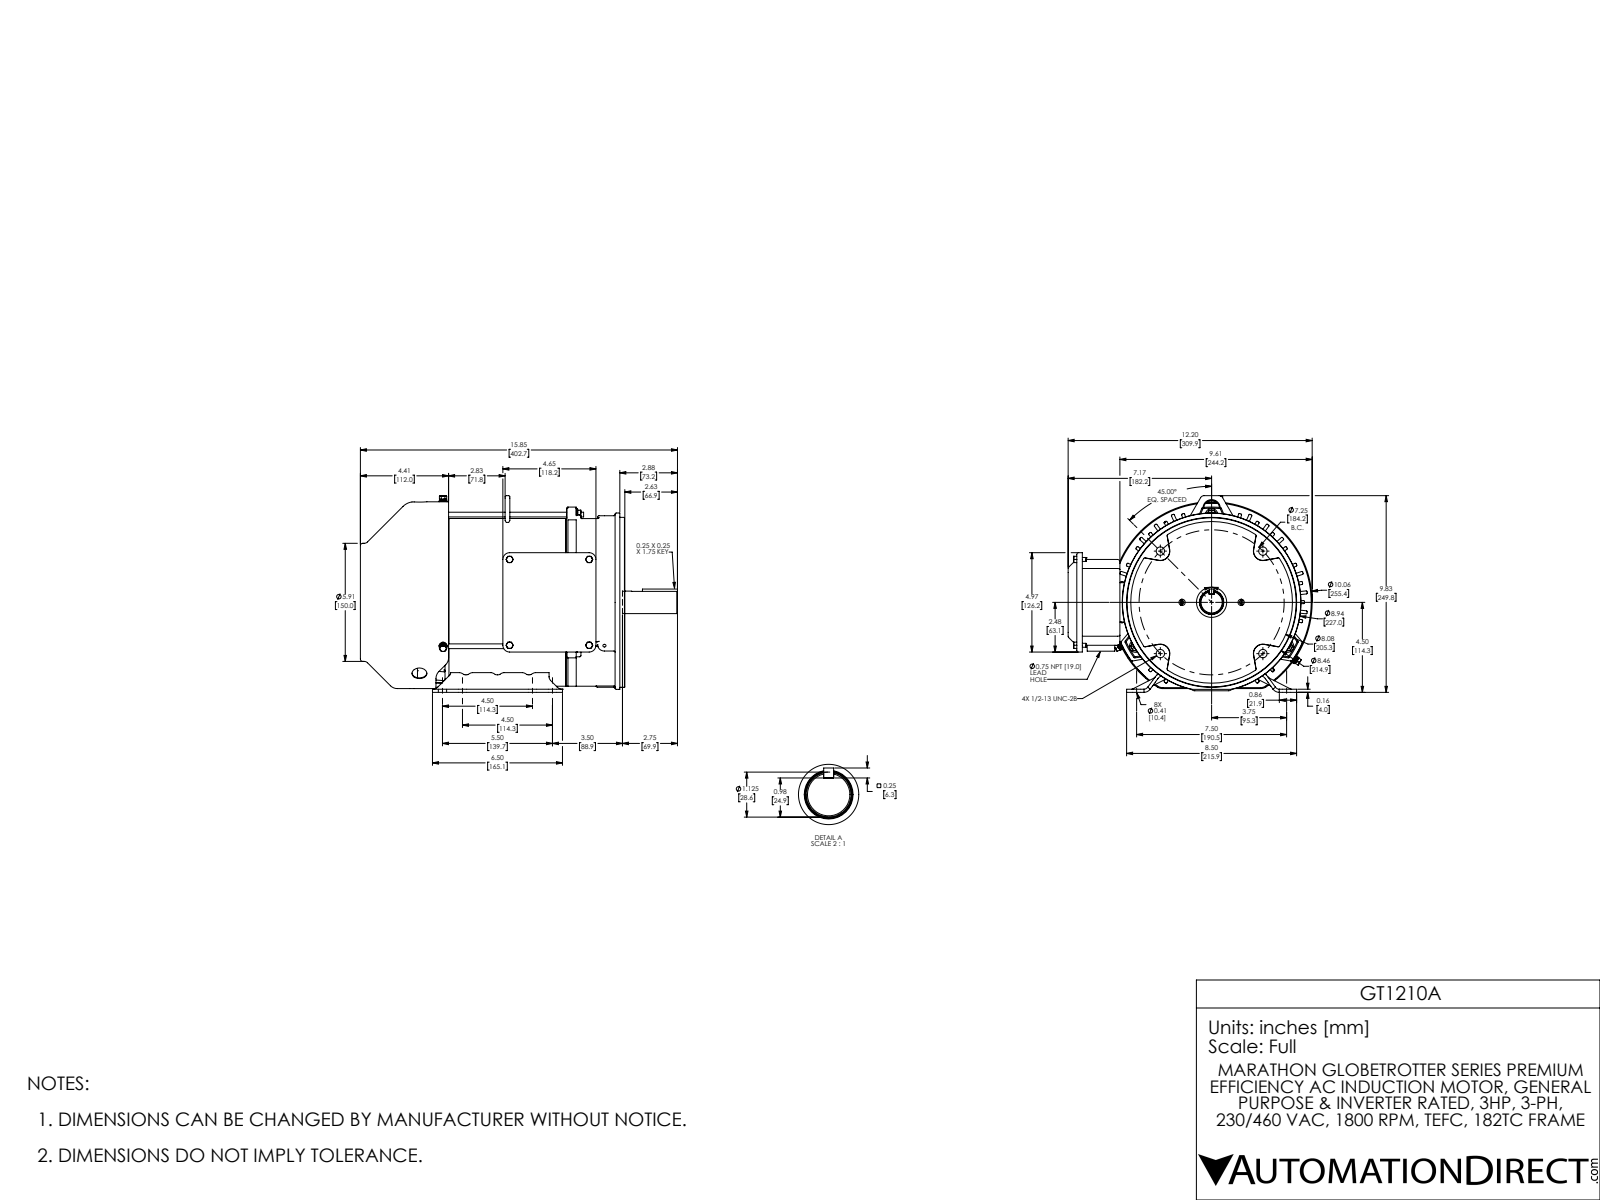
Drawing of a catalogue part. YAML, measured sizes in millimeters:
part_name: "SS600200-182TC_RevB r1 2 surfs rep Nice r3 -fan ext bell 1 R1 finext 1 -FBell b2 r1 COMB 1 COMPLETE 1 with 600198 BBELLS 1 work pre Coord RED 1"
step_written_by: "SolidWorks 2017 (AUTOMOTIVE_DESIGN)"
units: millimeters
bodies: {solids: 30, faces: 4408, planar: 645, cylindrical: 1681, other: 2082}
overall_size: [402.7, 309.9, 249.8]
volume: 4472000
surface_area: 979400
round_holes:
  - {diameter: 4.2, count: 8}
  - {diameter: 10.5, count: 8}
  - {diameter: 8, count: 6}
  - {diameter: 5, count: 4}
  - {diameter: 5.5, count: 4}
  - {diameter: 10.7, count: 4}
  - {diameter: 5.3, count: 3}
  - {diameter: 6.4, count: 3}
  - {diameter: 7, count: 3}
  - {diameter: 3.3, count: 2}
  - {diameter: 19, count: 2}
  - {diameter: 5.8, count: 1}
round_bosses_or_shafts:
  - {diameter: 5, count: 7}
  - {diameter: 15.5, count: 3}
  - {diameter: 10, count: 3}
  - {diameter: 6, count: 3}
  - {diameter: 255.4, count: 1}
  - {diameter: 227, count: 1}
  - {diameter: 215.9, count: 1}
  - {diameter: 213, count: 1}
partial_cylinders:
  - {radius: 1.5, count: 212}
  - {radius: 1, count: 120}
  - {radius: 33.5, count: 72}
  - {radius: 36, count: 72}
  - {radius: 2, count: 31}
  - {radius: 1.2, count: 28}
  - {radius: 2.4, count: 28}
  - {radius: 6, count: 18}
face_to_face_distances: [1.2, 198.6, 2, 4, 64.5, 188.3, 288.1, 99.8, 21.8, 176.8]
hole_center_spacings: [20, 25.4, 28.3, 61.2, 62.5, 70.7, 74.3, 89.1]
